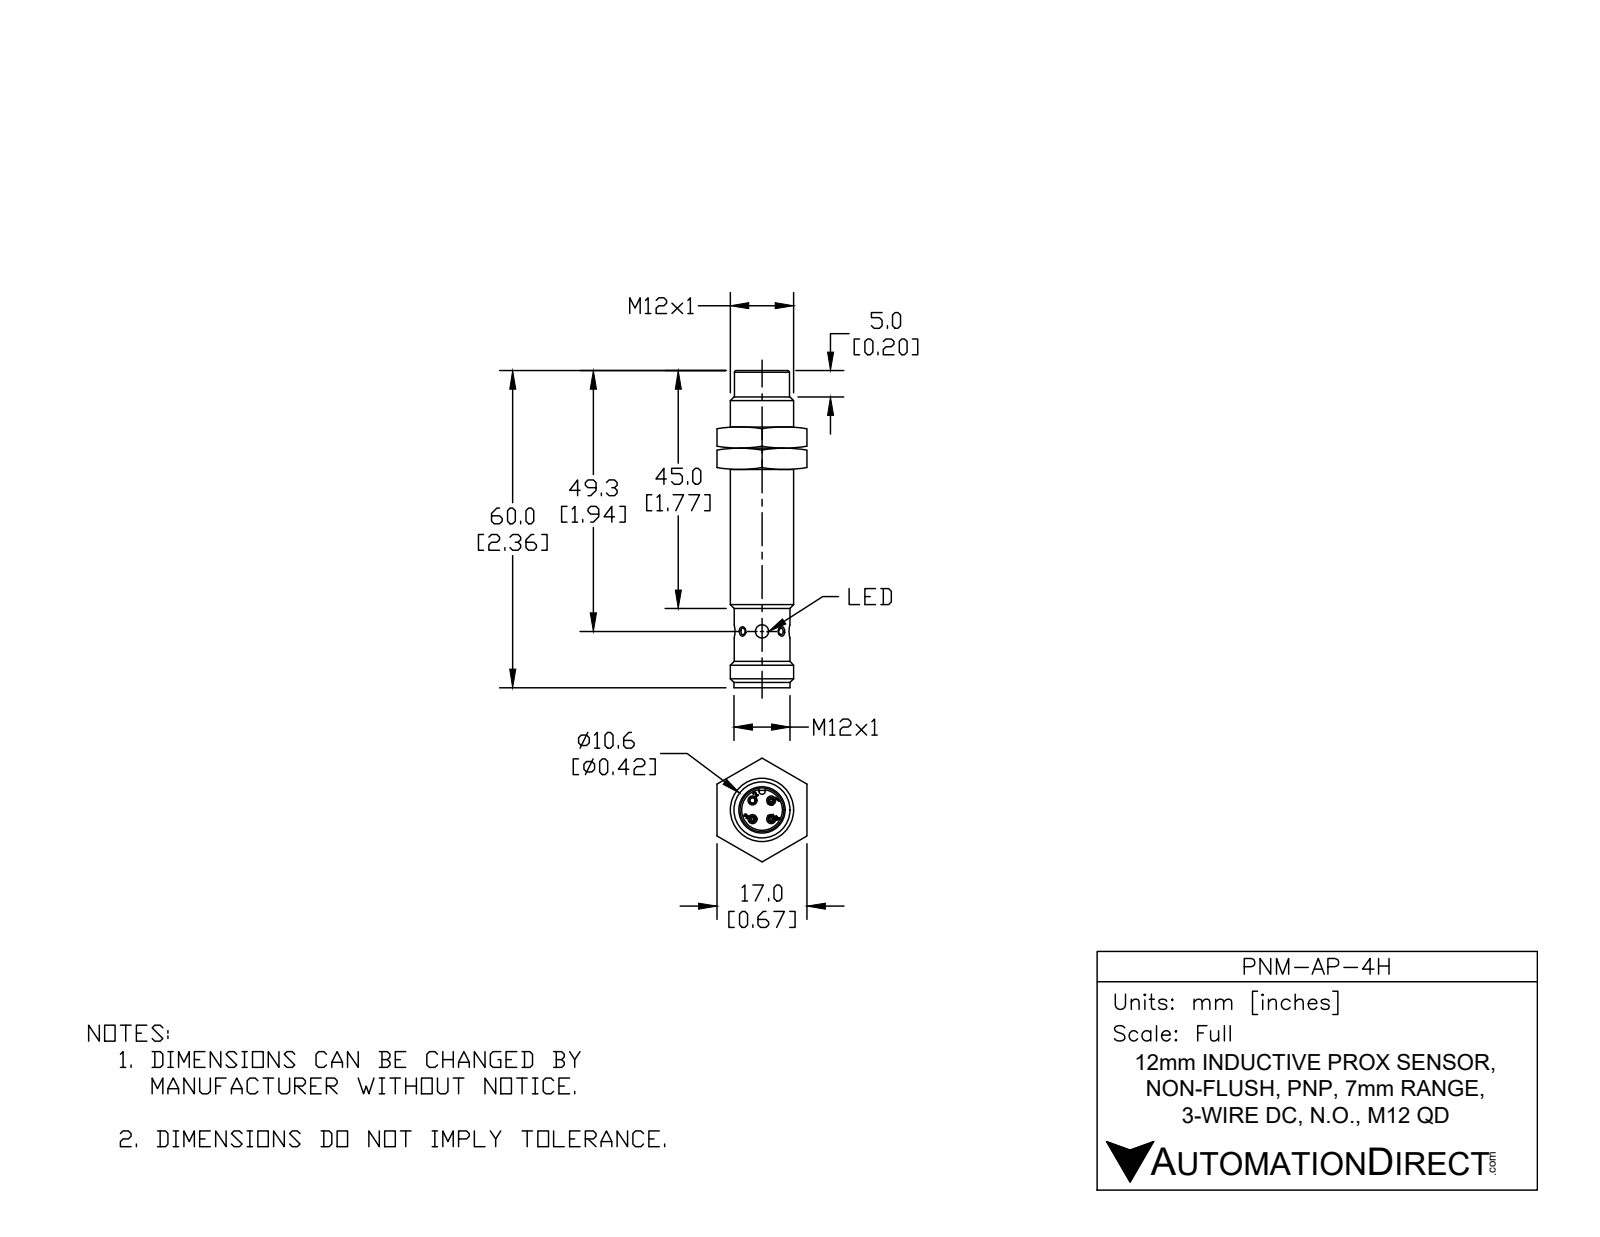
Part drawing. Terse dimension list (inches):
name: PNM-AP-4H
written by: SolidWorks 2017 (AUTOMOTIVE_DESIGN)
unit: in
bodies: 1 solid, 479 faces (119 planar, 134 cylindrical, 226 other)
size: 2.362 × 0.472 × 0.472
volume: 0.35 in³; area: 10.25 in²
holes: 3× ⌀0.043, 2× ⌀0.04, 2× ⌀0.098, 1× ⌀0.038, 1× ⌀0.04, 1× ⌀0.327, 1× ⌀0.394, 1× ⌀0.401
bosses: 9× ⌀0.039, 1× ⌀0.472, 1× ⌀0.417, 1× ⌀0.415, 1× ⌀0.4, 1× ⌀0.392, 1× ⌀0.39, 1× ⌀0.376
rounds: 36× R0.004, 1× R0.024, 1× R0.031, 1× R0.161
face distances: 0.039, 1.87, 1.831, 0.018, 0.022, 1.852, 2.323, 0.142, 2.012, 1.994
hole spacings: 0.098, 0.139, 0.197
